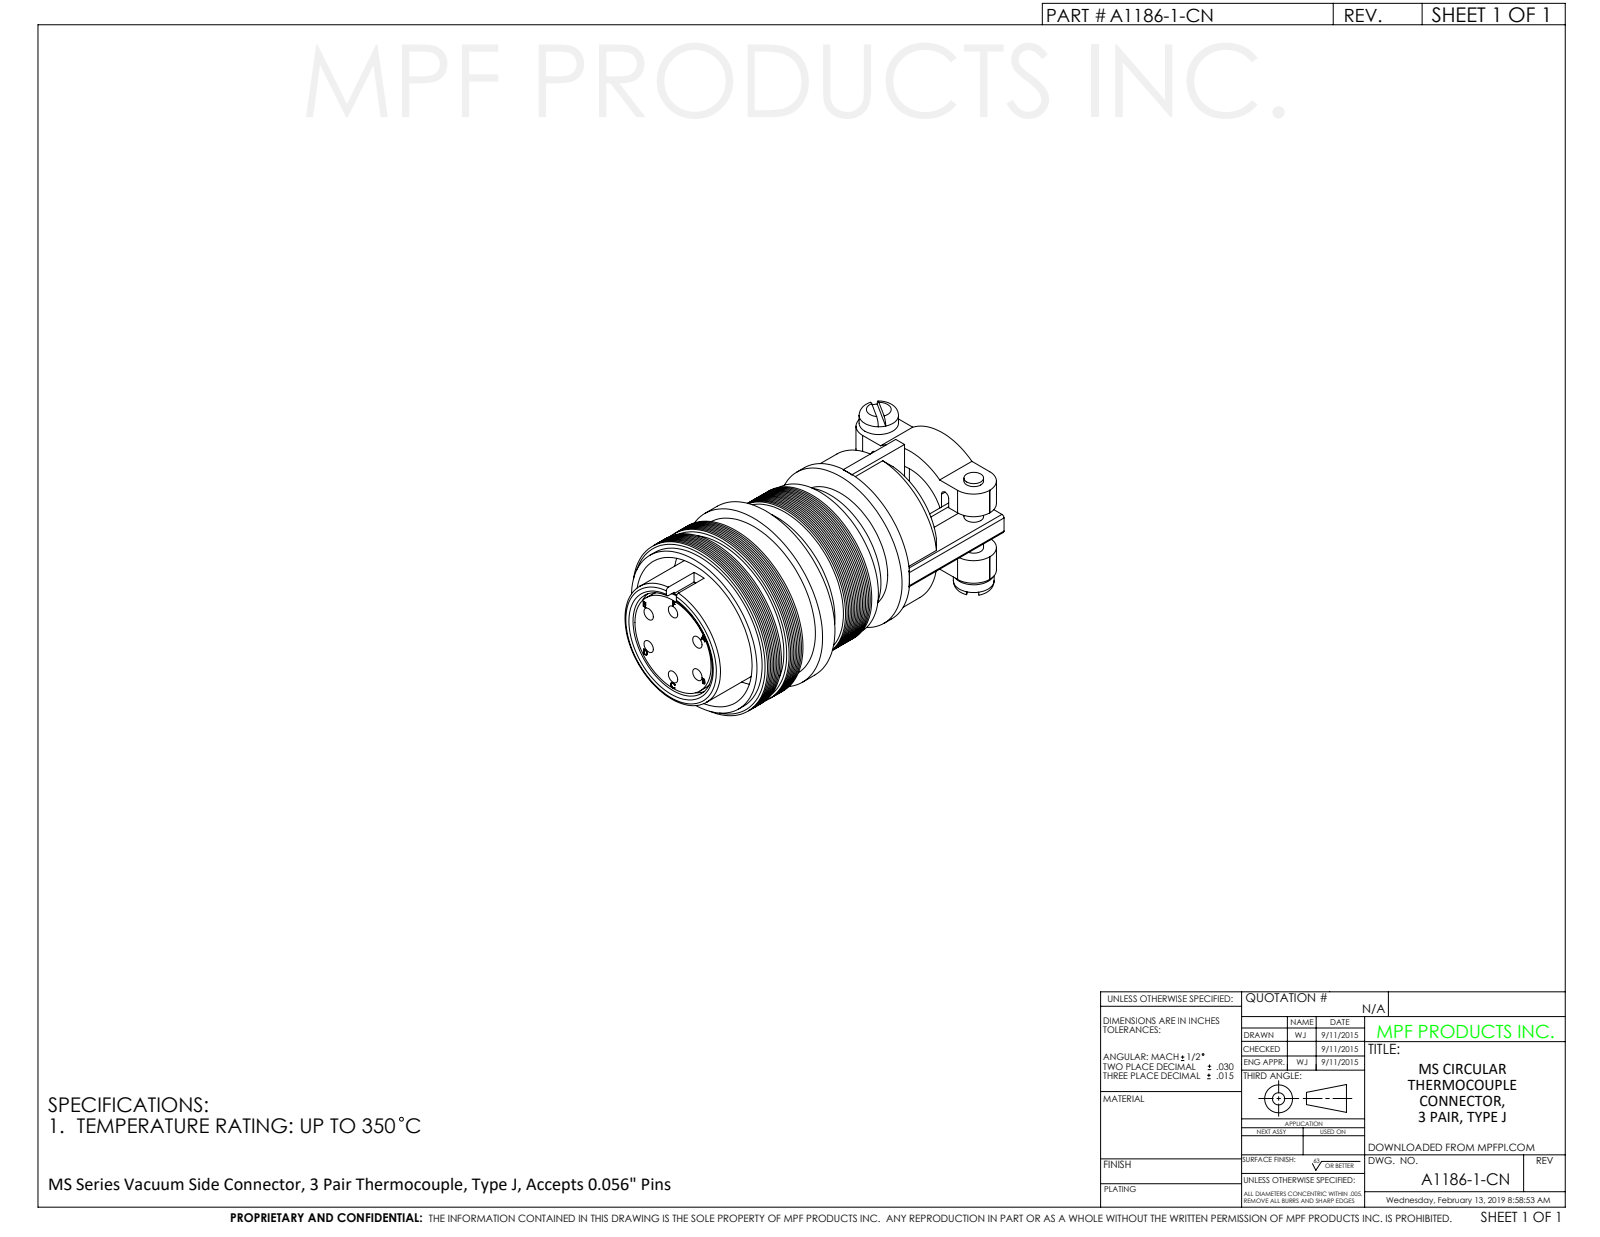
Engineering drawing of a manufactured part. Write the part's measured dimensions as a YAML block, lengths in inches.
part_name: "A1136-3-CN"
step_written_by: "SolidWorks 2012 (CONFIG_CONTROL_DESIGN)"
units: inches
bodies: {solids: 1, faces: 380, planar: 107, cylindrical: 91, other: 182}
overall_size: [2.637, 1.34, 1.34]
volume: 2.227
surface_area: 23.13
round_holes:
  - {diameter: 0.091, count: 6}
  - {diameter: 0.646, count: 1}
  - {diameter: 0.78, count: 1}
  - {diameter: 1.125, count: 1}
round_bosses_or_shafts:
  - {diameter: 0.135, count: 2}
  - {diameter: 1.34, count: 1}
  - {diameter: 1.223, count: 1}
  - {diameter: 1.22, count: 1}
  - {diameter: 1.2, count: 1}
  - {diameter: 1.14, count: 1}
  - {diameter: 0.99, count: 1}
  - {diameter: 0.92, count: 1}
partial_cylinders:
  - {radius: 0.034, count: 8}
  - {radius: 0.02, count: 4}
  - {radius: 0.156, count: 4}
  - {radius: 0.472, count: 1}
  - {radius: 0.473, count: 1}
face_to_face_distances: [1.193, 0.643, 0.47, 0.722, 0.1, 0.2, 0.522, 0.992, 1.714, 2.618]
hole_center_spacings: [0.273, 0.473, 0.546]
